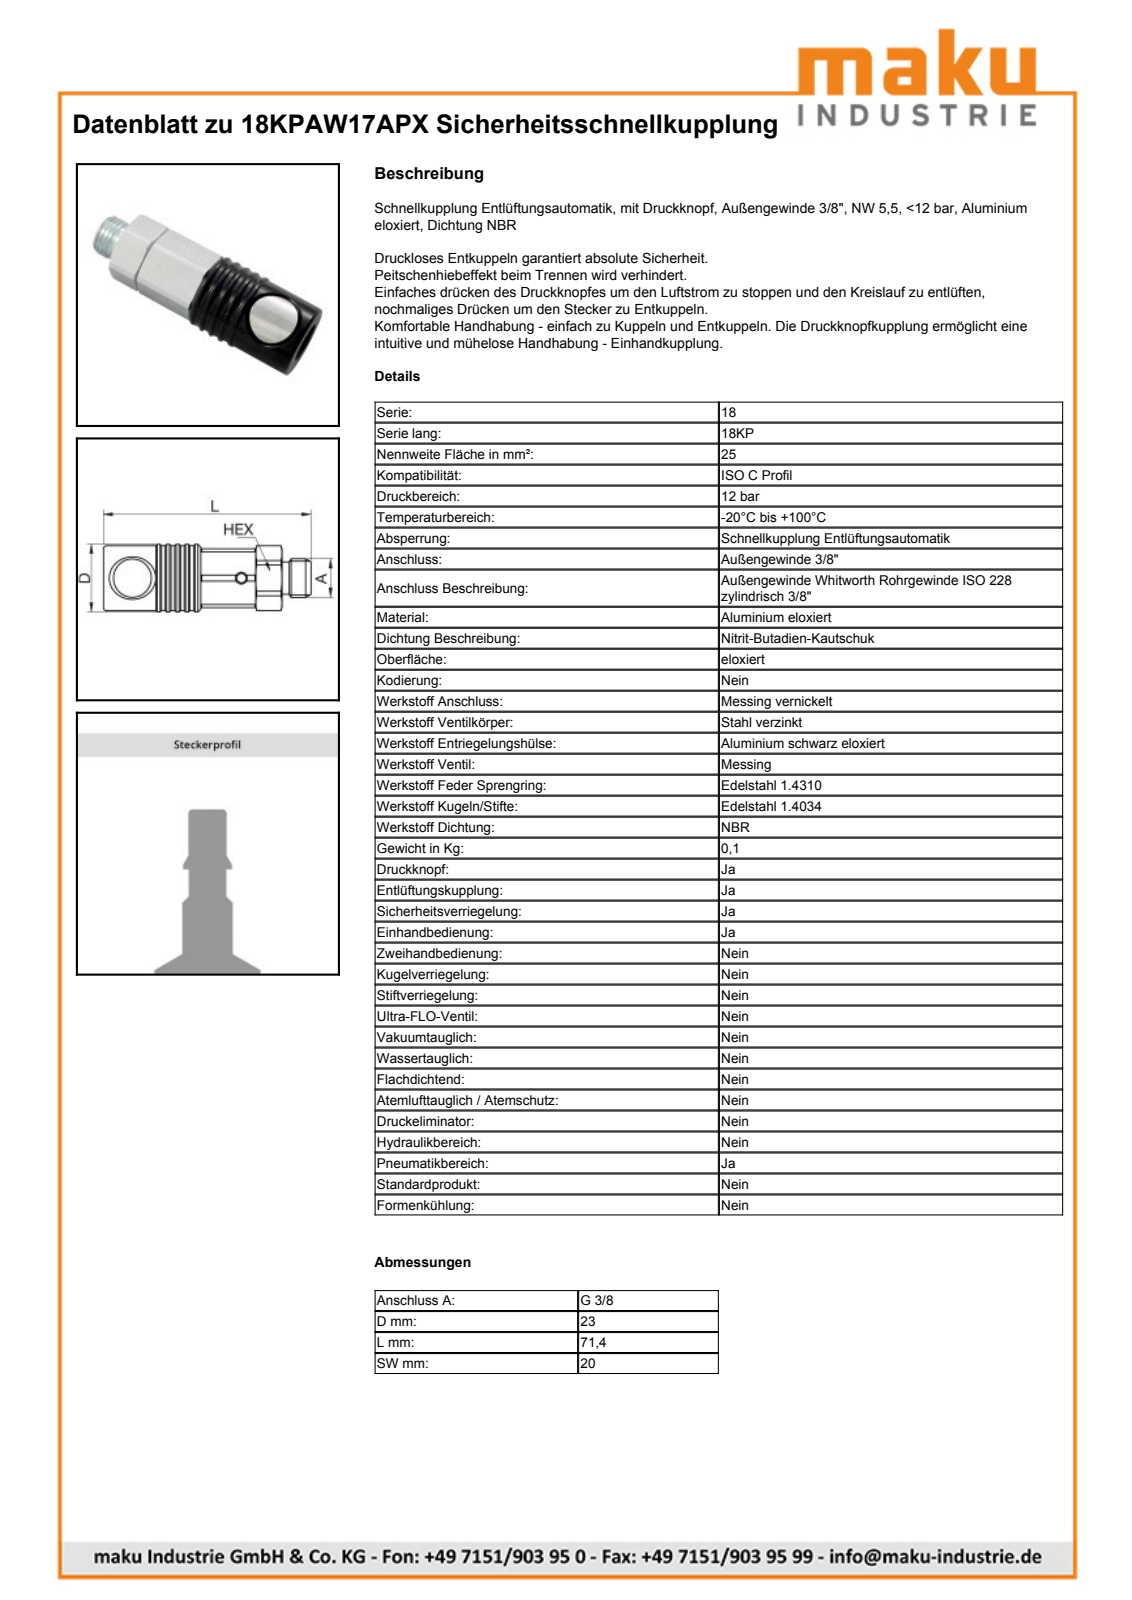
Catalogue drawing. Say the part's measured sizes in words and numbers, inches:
The part is named "18KPAW17APX". Its 3-D file was written by "Autodesk Inventor 2019 (CONFIG_CONTROL_DESIGN)". It is 27 solids with 303 faces: 96 planar, 105 cylindrical and 102 other. Overall it measures 2.811 by 0.906 by 0.906 inches. Its volume is 1.942 cubic inches and its surface area 31.29 square inches. Round holes: 1 of diameter 0.098, 1 of diameter 0.138, 1 of diameter 0.217, 1 of diameter 0.276, 1 of diameter 0.335, 1 of diameter 0.398, 1 of diameter 0.409, 1 of diameter 0.413, 1 of diameter 0.437, 1 of diameter 0.472, 1 of diameter 0.508, 1 of diameter 0.553. Round bosses or shafts: 1 of diameter 0.906, 1 of diameter 0.866, 1 of diameter 0.787, 1 of diameter 0.728, 1 of diameter 0.717, 1 of diameter 0.709, 1 of diameter 0.687, 1 of diameter 0.656. Partial cylindrical surfaces (rounded edges, fillets, slot ends): 1 of radius 0.148, 1 of radius 0.284, 1 of radius 0.307, 1 of radius 0.433, 1 of radius 0.487. The main face-to-face distances are 0.787, 2.063, 0.748, 1.157, 0.394, 0.906, 0.433, 0.177, 0.276, 0.098. The hole center spacings are 0.047, 0.049, 1.474.
